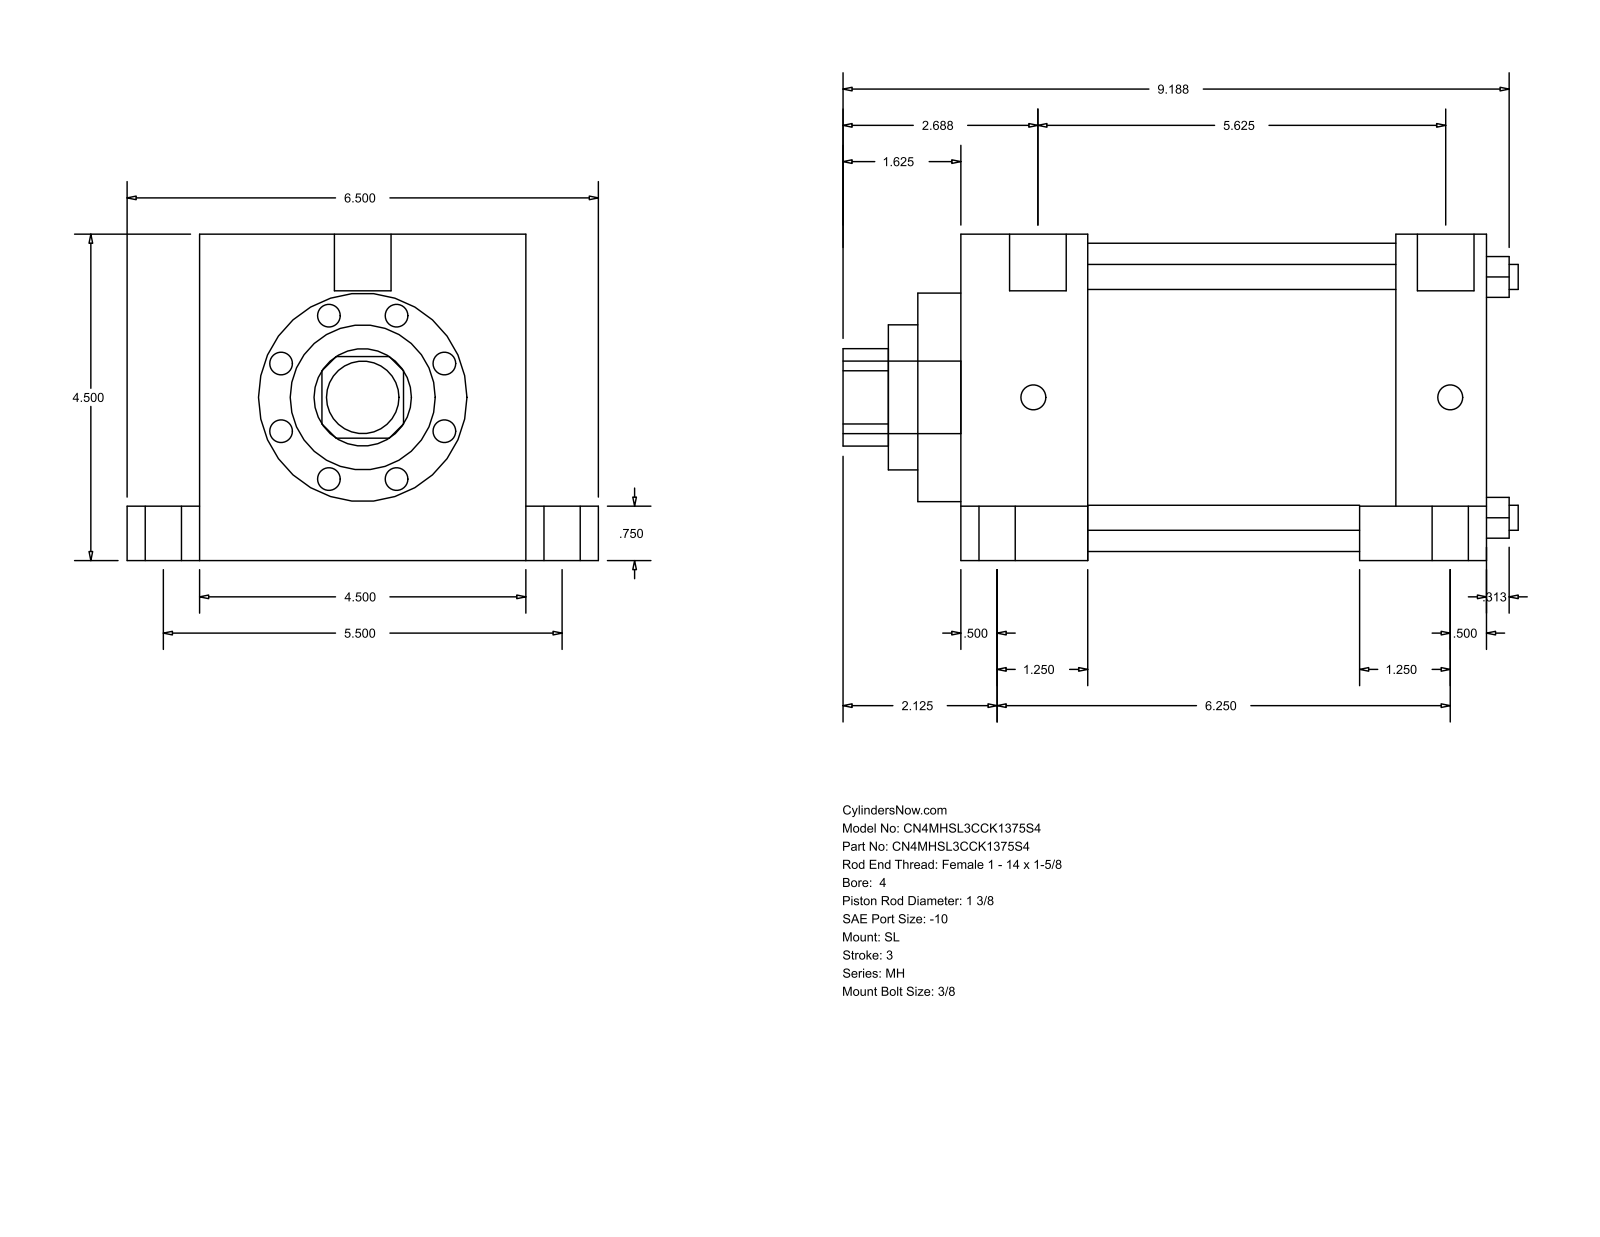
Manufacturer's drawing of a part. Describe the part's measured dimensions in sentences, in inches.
The part is named "MH_SL__0400_1.375". Its 3-D file was written by "GSSL Pune (CONFIG_CONTROL_DESIGN)". It is 0 solids with 110 faces: 77 planar, 33 cylindrical and 0 other. Overall it measures 9.313 by 6.5 by 4.5 inches. Round holes: 4 of diameter 0.345, 1 of diameter 1.375, 1 of diameter 2, 1 of diameter 2.875, 1 of diameter 4.25. Round bosses or shafts: 4 of diameter 0.75, 4 of diameter 0.5, 4 of diameter 0.344, 2 of diameter 0.781, 1 of diameter 1. Partial cylindrical surfaces (rounded edges, fillets, slot ends): 1 of radius 0.672. The main face-to-face distances are 4.5, 7.25, 1.75, 5.5, 5.5, 3.75, 6, 4.25, 1.25, 1. The hole center spacings are 2.347, 3.32, 4.695.
